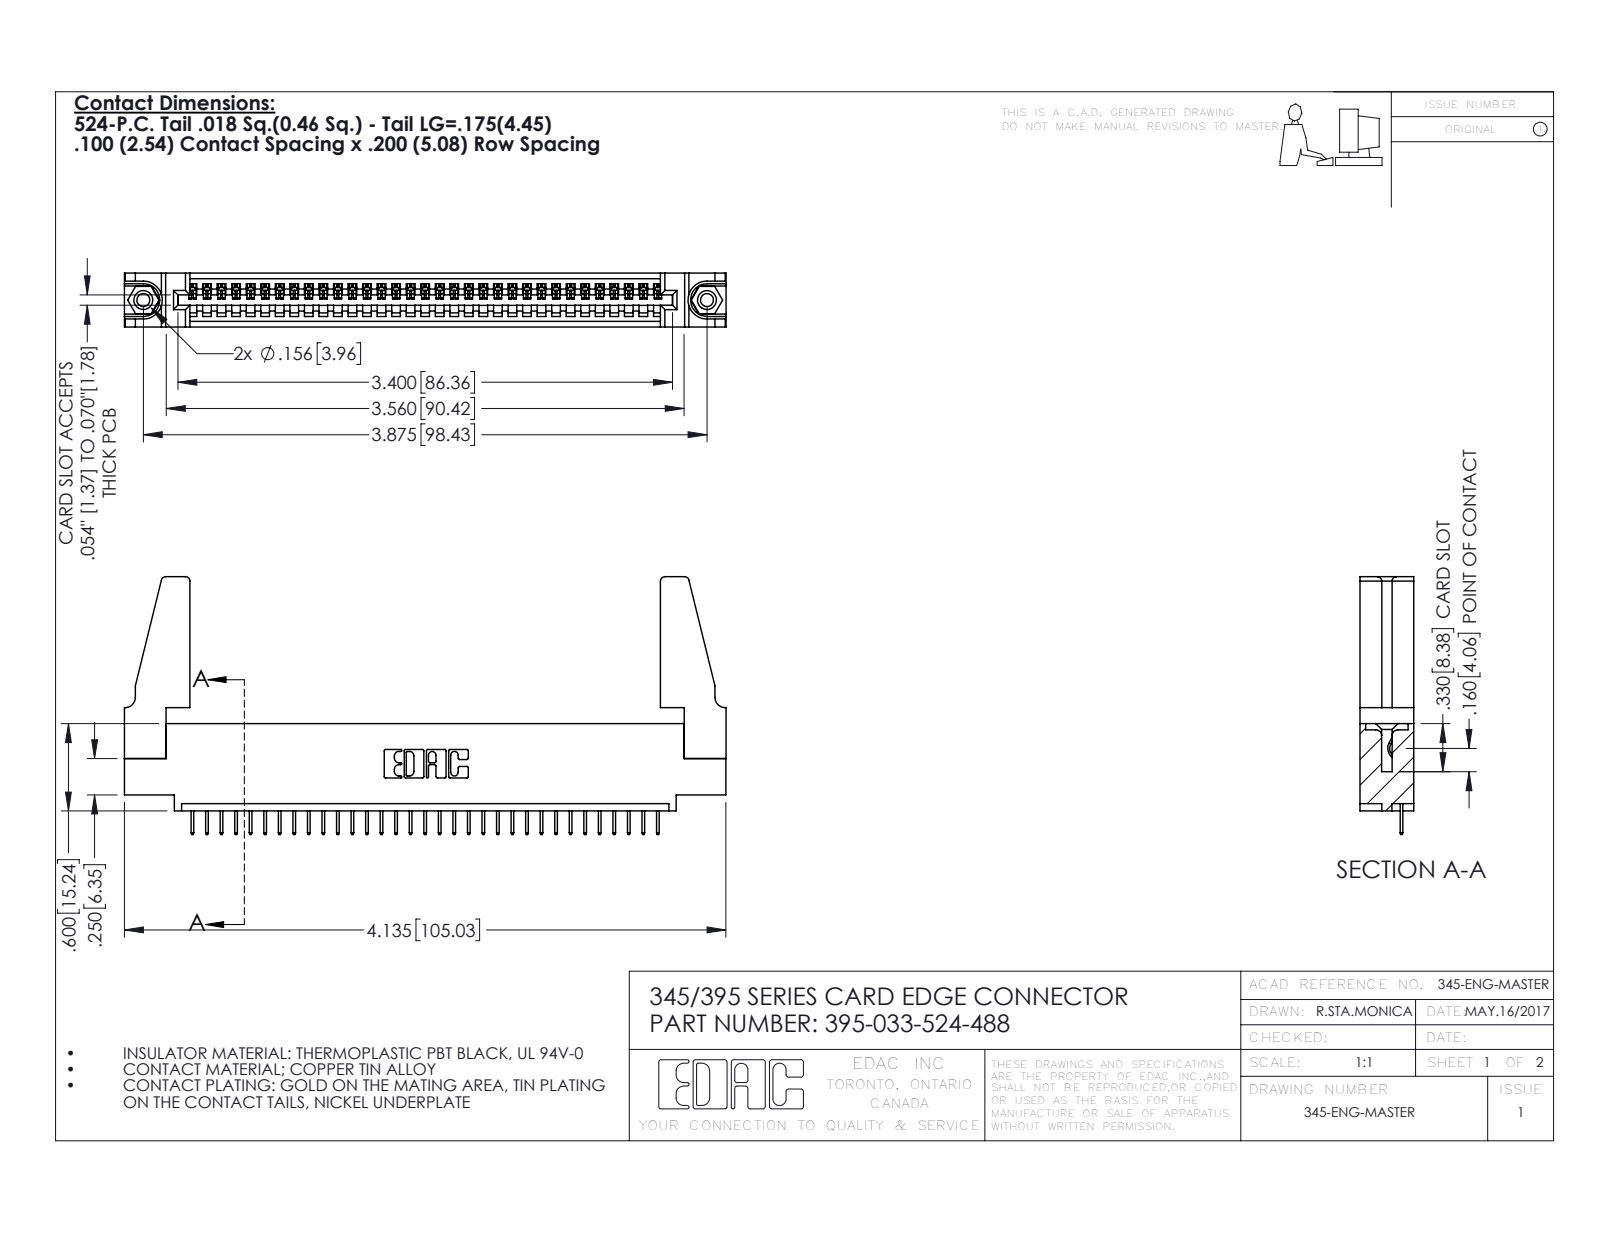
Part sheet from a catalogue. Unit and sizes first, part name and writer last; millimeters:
Units: millimetres
Overall size (bounding box): 105.1 × 45 × 9.4
Round holes (diameter × count): ⌀2.3 ×2, ⌀3.2 ×2, ⌀4 ×2, ⌀1.6 ×1
Round bosses / shafts (diameter × count): ⌀3.9 ×2
Partial cylindrical surfaces — rounded edges, fillets, slot ends (radius × count): R0.2 ×66, R0.3 ×22, R0.8 ×8, R0.2 ×6, R0.8 ×6, R0.7 ×3, R0.8 ×2, R1 ×2
Main face-to-face distances: 1.8, 9.4, 7.6, 5.1, 2.5, 6.9, 0.6, 5.7, 1.8, 3.8
Hole centre spacings: 6.9, 92.5, 98.4
Volume: 12 900 mm³ · Surface area: 15 560 mm²
Bodies: 38 solids, 2300 faces (1674 planar, 610 cylindrical, 16 other)
Part name (STEP PRODUCT): 395-033-524-488; 345-250-001_345-250-001-102; 345 Part_0.110 Offset - 0.156 Dia-TH; 345-292-001_345-293-124 (+1 more)
STEP written by: SolidWorks 2016 (CONFIG_CONTROL_DESIGN)
